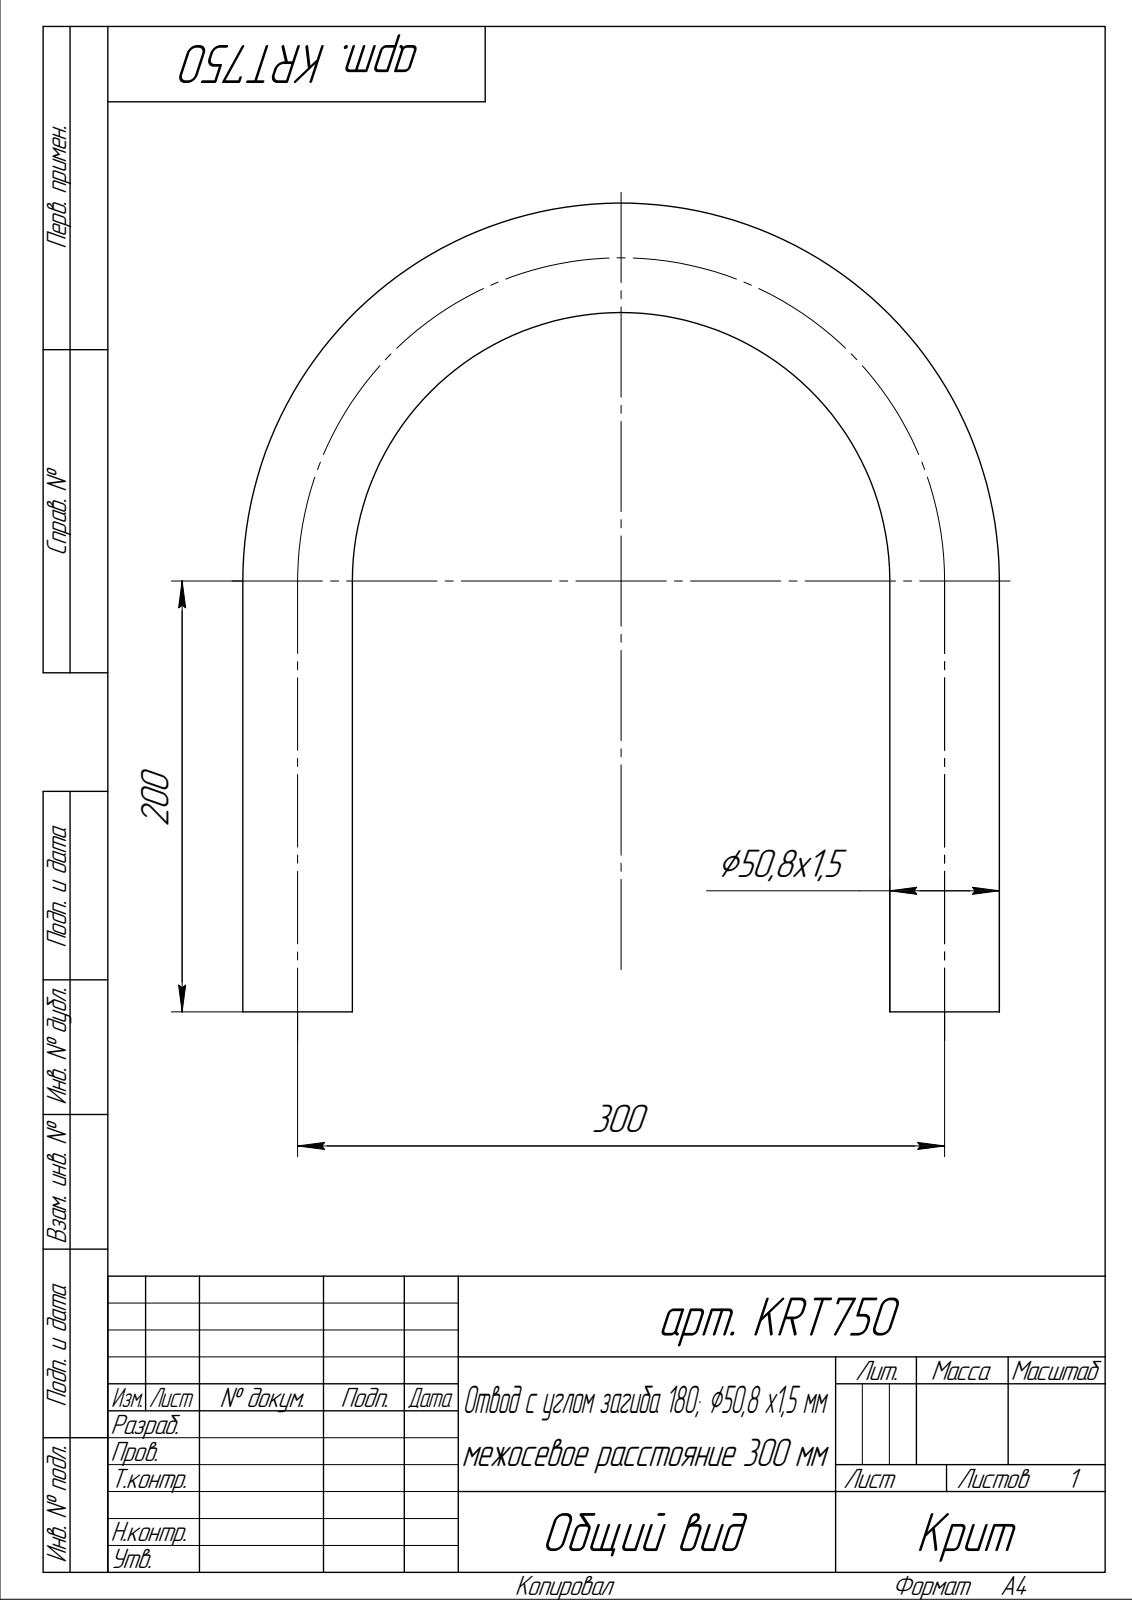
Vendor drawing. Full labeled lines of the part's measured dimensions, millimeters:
Part name (STEP PRODUCT): Деталь
STEP written by: ASCON Math Kernel (AUTOMOTIVE_DESIGN)
Units: millimetres
Bodies: 1 solid, 8 faces (2 planar, 4 cylindrical, 2 other)
Overall size (bounding box): 375.4 × 350.8 × 50.8
Volume: 202 407 mm³ · Surface area: 270 340 mm²
Round holes (diameter × count): ⌀47.8 ×2
Round bosses / shafts (diameter × count): ⌀50.8 ×2
Hole centre spacings: 300
